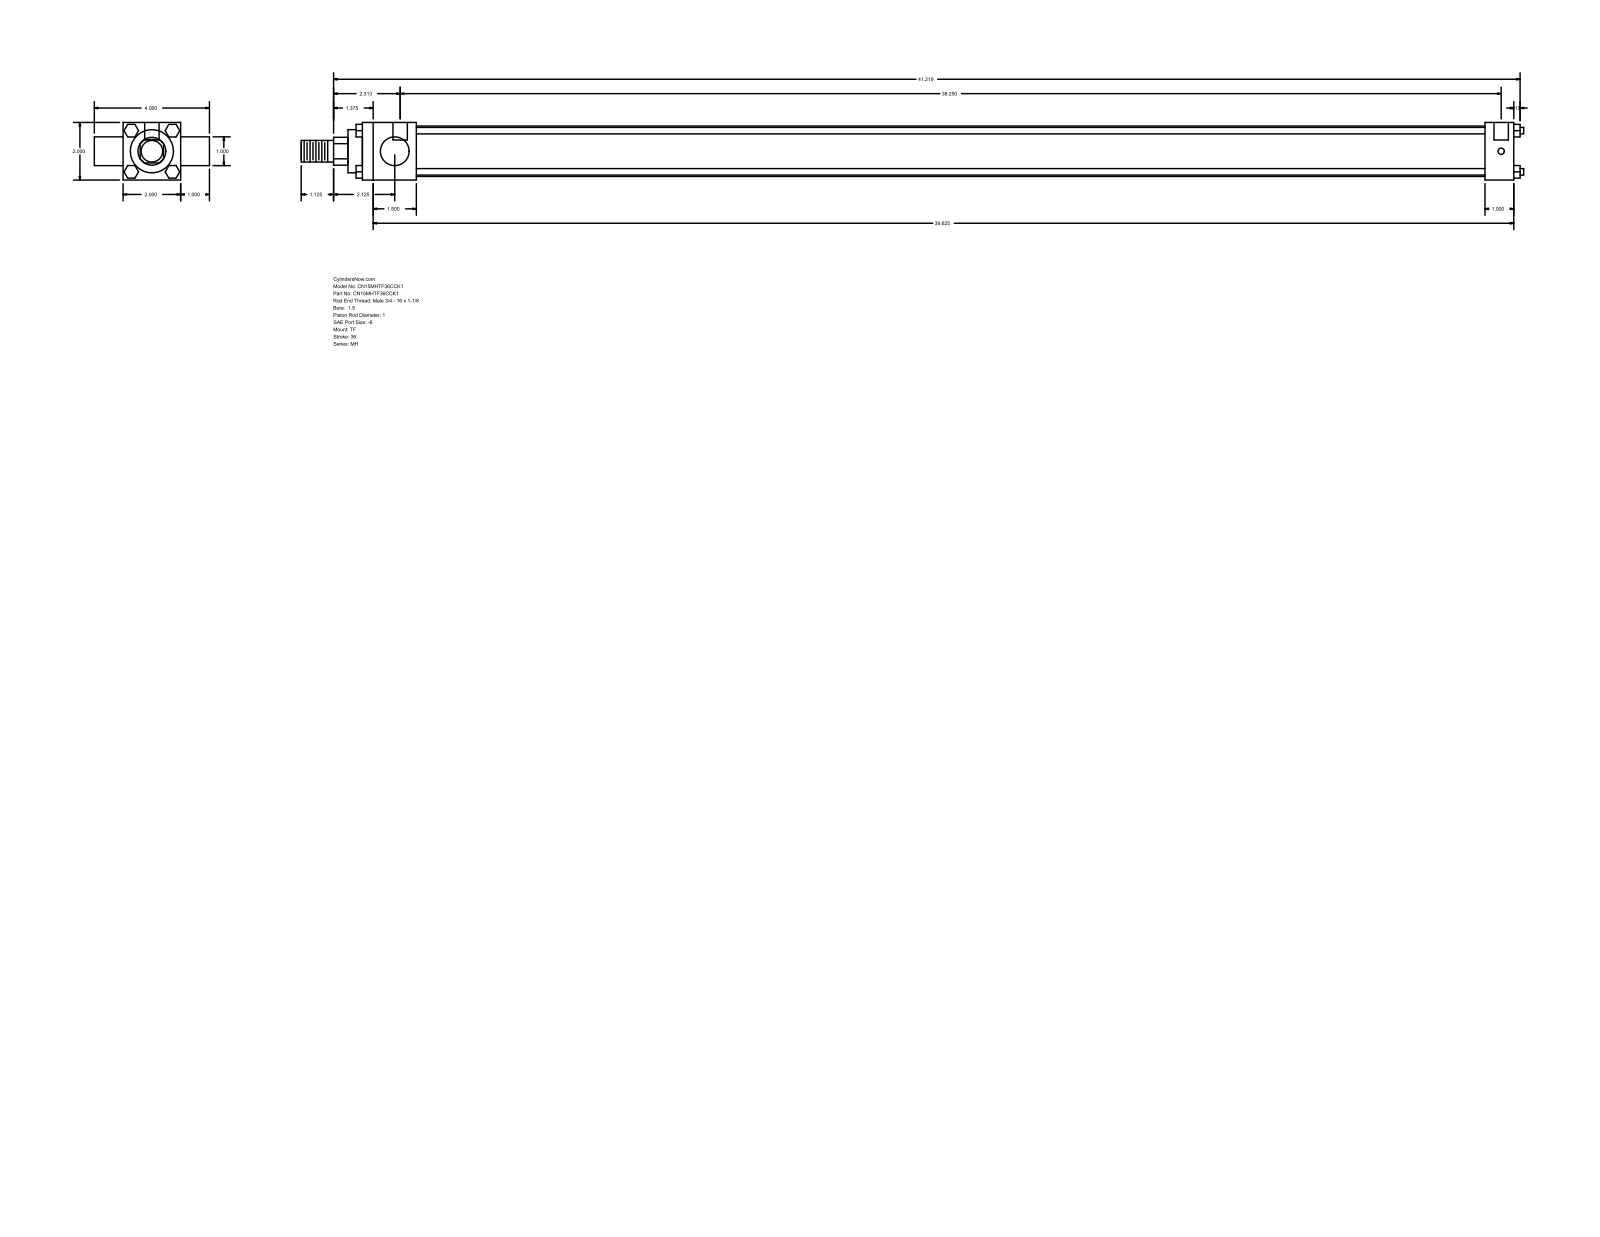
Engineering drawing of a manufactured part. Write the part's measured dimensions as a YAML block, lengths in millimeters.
part_name: "MH_TF__0150_1"
step_written_by: "GSSL Pune (CONFIG_CONTROL_DESIGN)"
units: millimeters
bodies: {solids: 0, faces: 120, planar: 92, cylindrical: 28, other: 0}
overall_size: [1078.71, 101.6, 50.8]
round_holes:
  - {diameter: 5.56, count: 3}
  - {diameter: 12.7, count: 2}
round_bosses_or_shafts:
  - {diameter: 5.71, count: 4}
  - {diameter: 25.4, count: 2}
  - {diameter: 44.45, count: 1}
  - {diameter: 38.1, count: 1}
  - {diameter: 19.05, count: 1}
partial_cylinders:
  - {radius: 12.29, count: 1}
face_to_face_distances: [50.8, 25.4, 1016, 76.2, 47.63, 968.37, 990.6, 942.97, 101.6, 12.7]
hole_center_spacings: [3.18, 971.55, 974.73]
